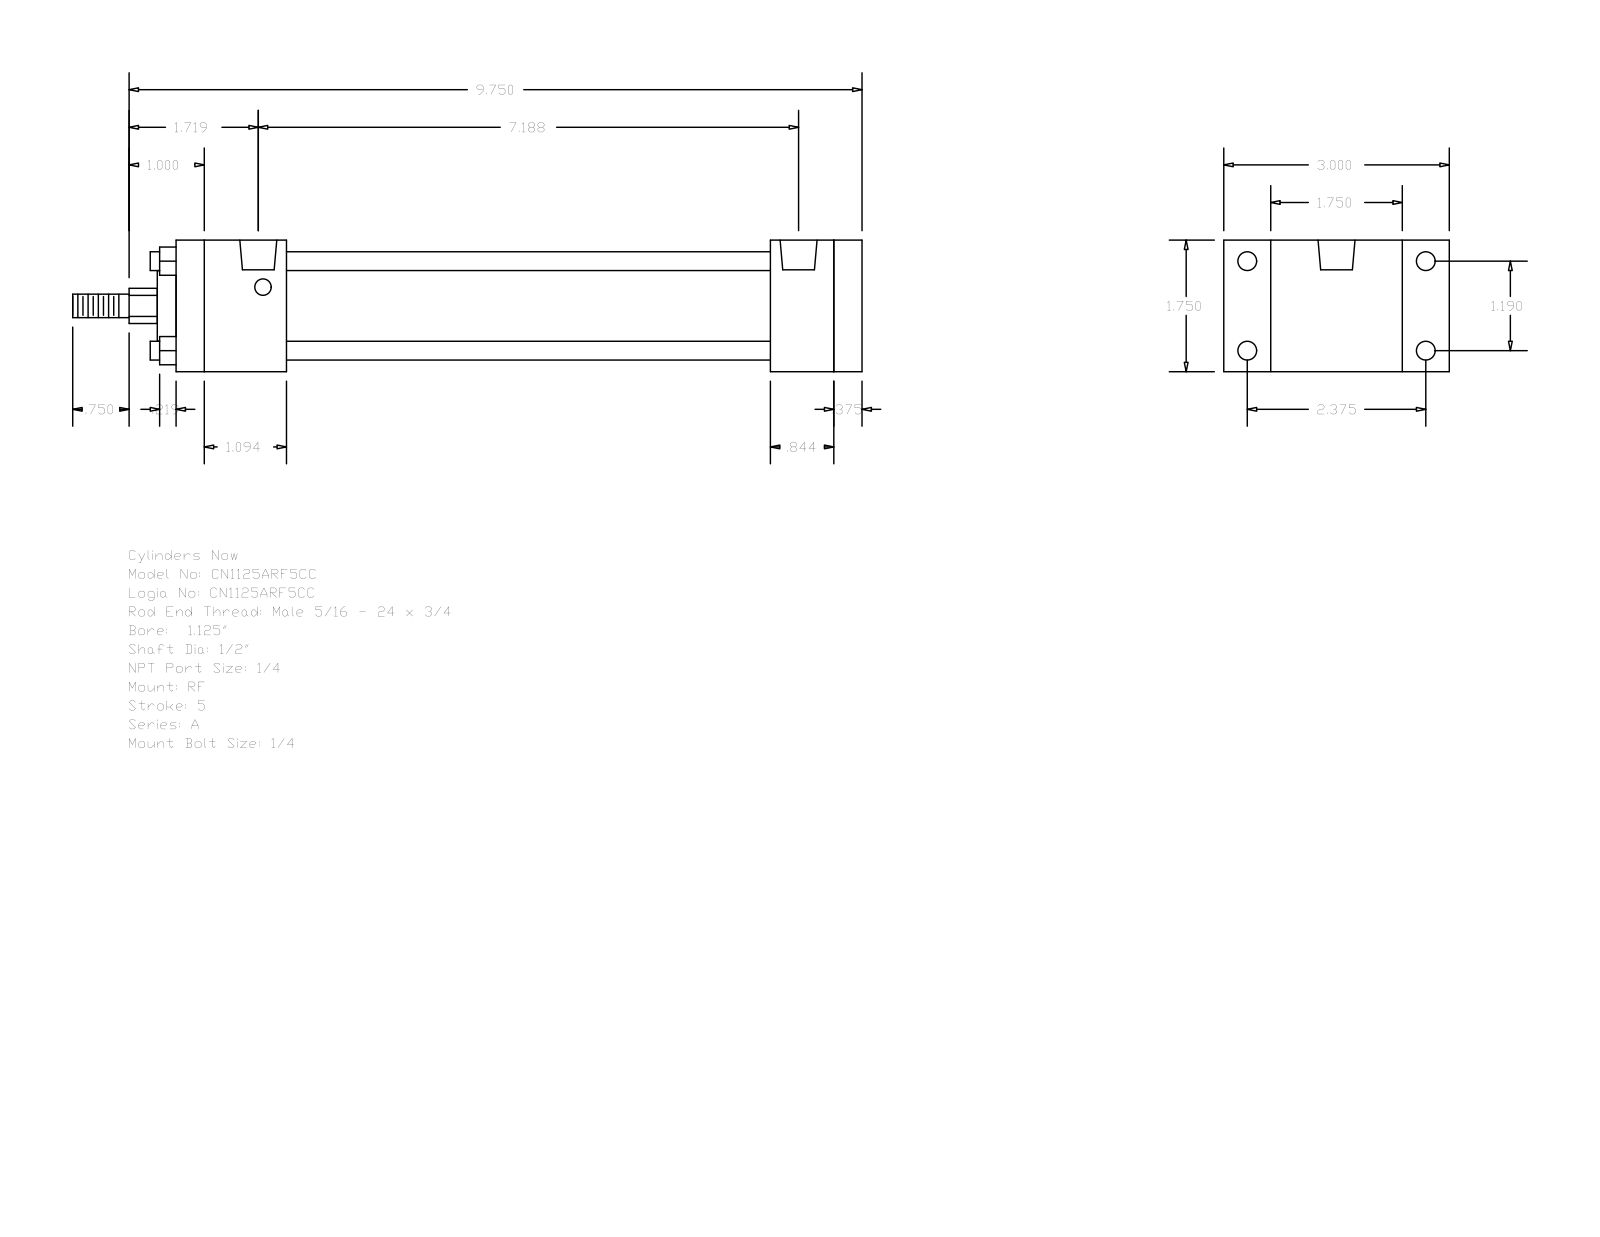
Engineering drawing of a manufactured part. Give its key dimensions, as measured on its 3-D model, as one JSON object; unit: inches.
{"part_name": "A_RF__0112_0.5", "step_written_by": "GSSL Pune (CONFIG_CONTROL_DESIGN)", "units": "inches", "bodies": {"solids": 0, "faces": 92, "planar": 64, "cylindrical": 28, "other": 0}, "overall_size": [10.5, 3, 1.75], "round_holes": [[0.219, 4], [0.25, 4], [0.492, 2]], "round_bosses_or_shafts": [[0.25, 4], [1.255, 1], [0.937, 1], [0.5, 1], [0.313, 1]], "partial_cylinders_radius": [[0.234, 1]], "face_to_face_distances": [1.75, 0.375, 9.125, 8.75, 1.469, 7.906, 6.437, 7.281, 7.656, 0.844], "hole_center_spacings": [1.19, 2.375, 2.656, 7.063, 0.062, 0.063, 7.125, 7.125]}
